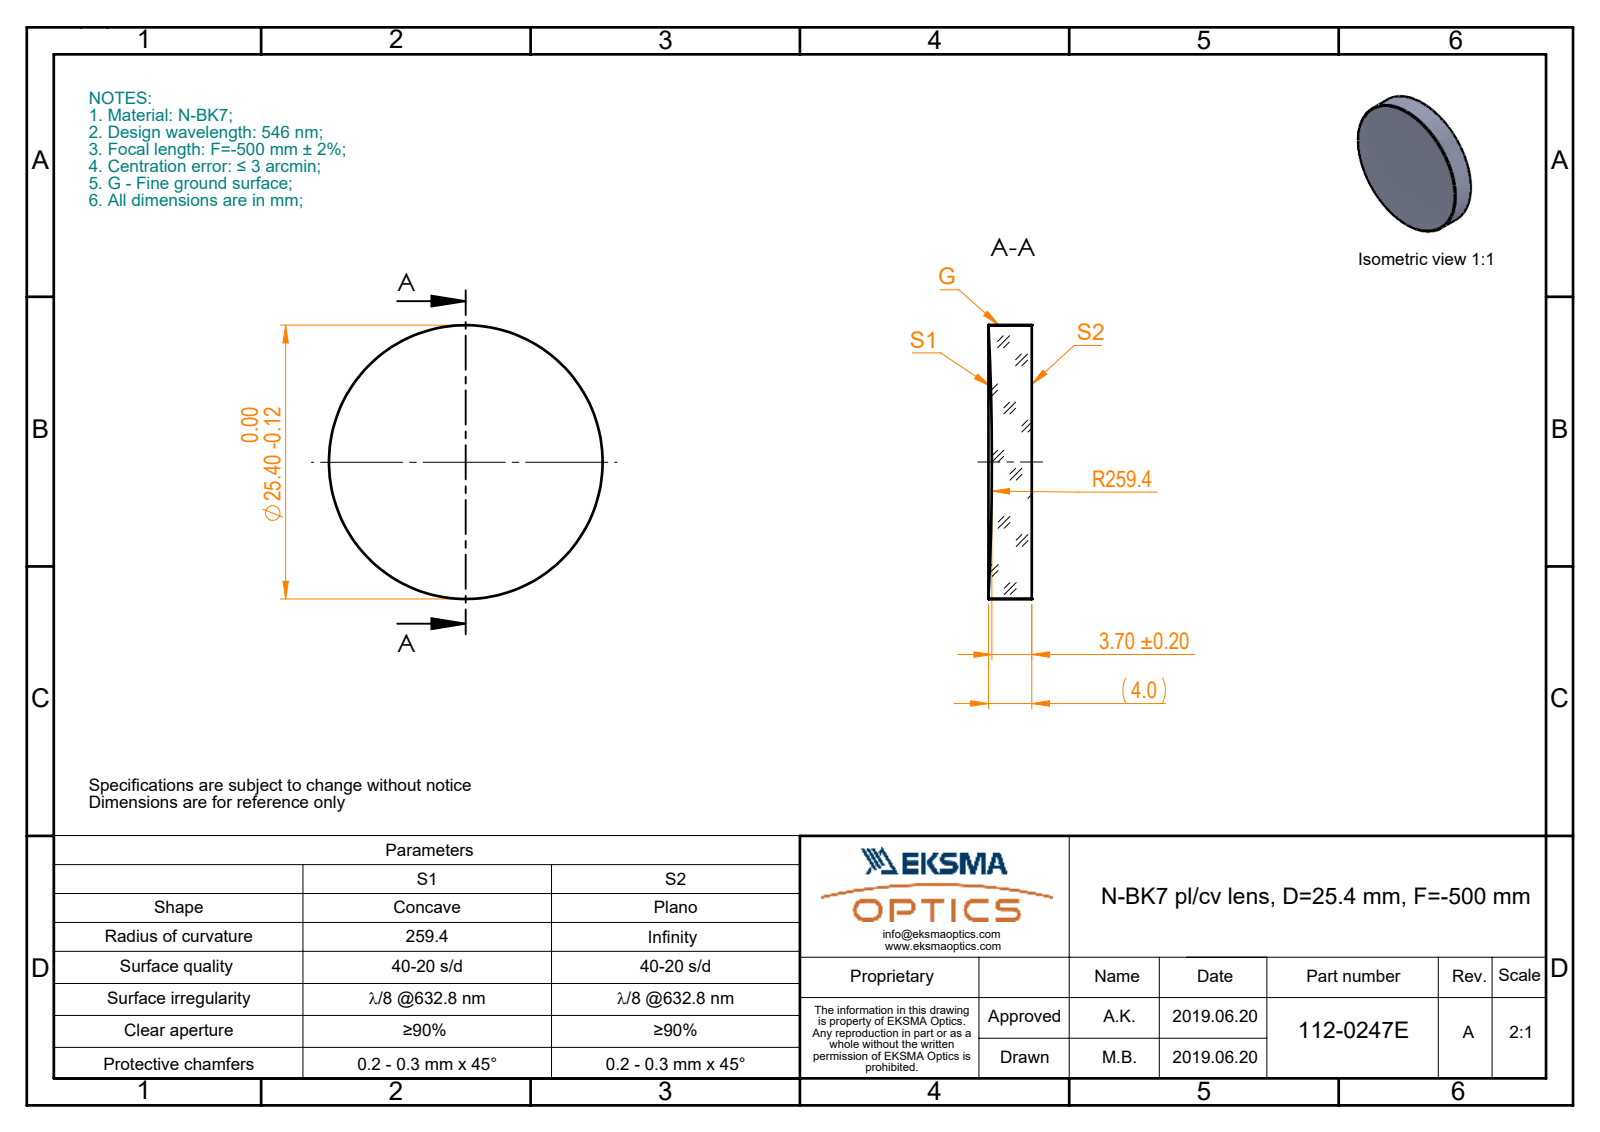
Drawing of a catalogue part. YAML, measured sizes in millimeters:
part_name: "112-0247E BK7 pl-cv 25.4 F-500"
step_written_by: "SolidWorks 2017 (CONFIG_CONTROL_DESIGN)"
units: millimeters
bodies: {solids: 1, faces: 5, planar: 1, cylindrical: 2, other: 2}
overall_size: [25.4, 25.4, 4.01]
volume: 1954
surface_area: 1334
round_bosses_or_shafts:
  - {diameter: 25.4, count: 1}
